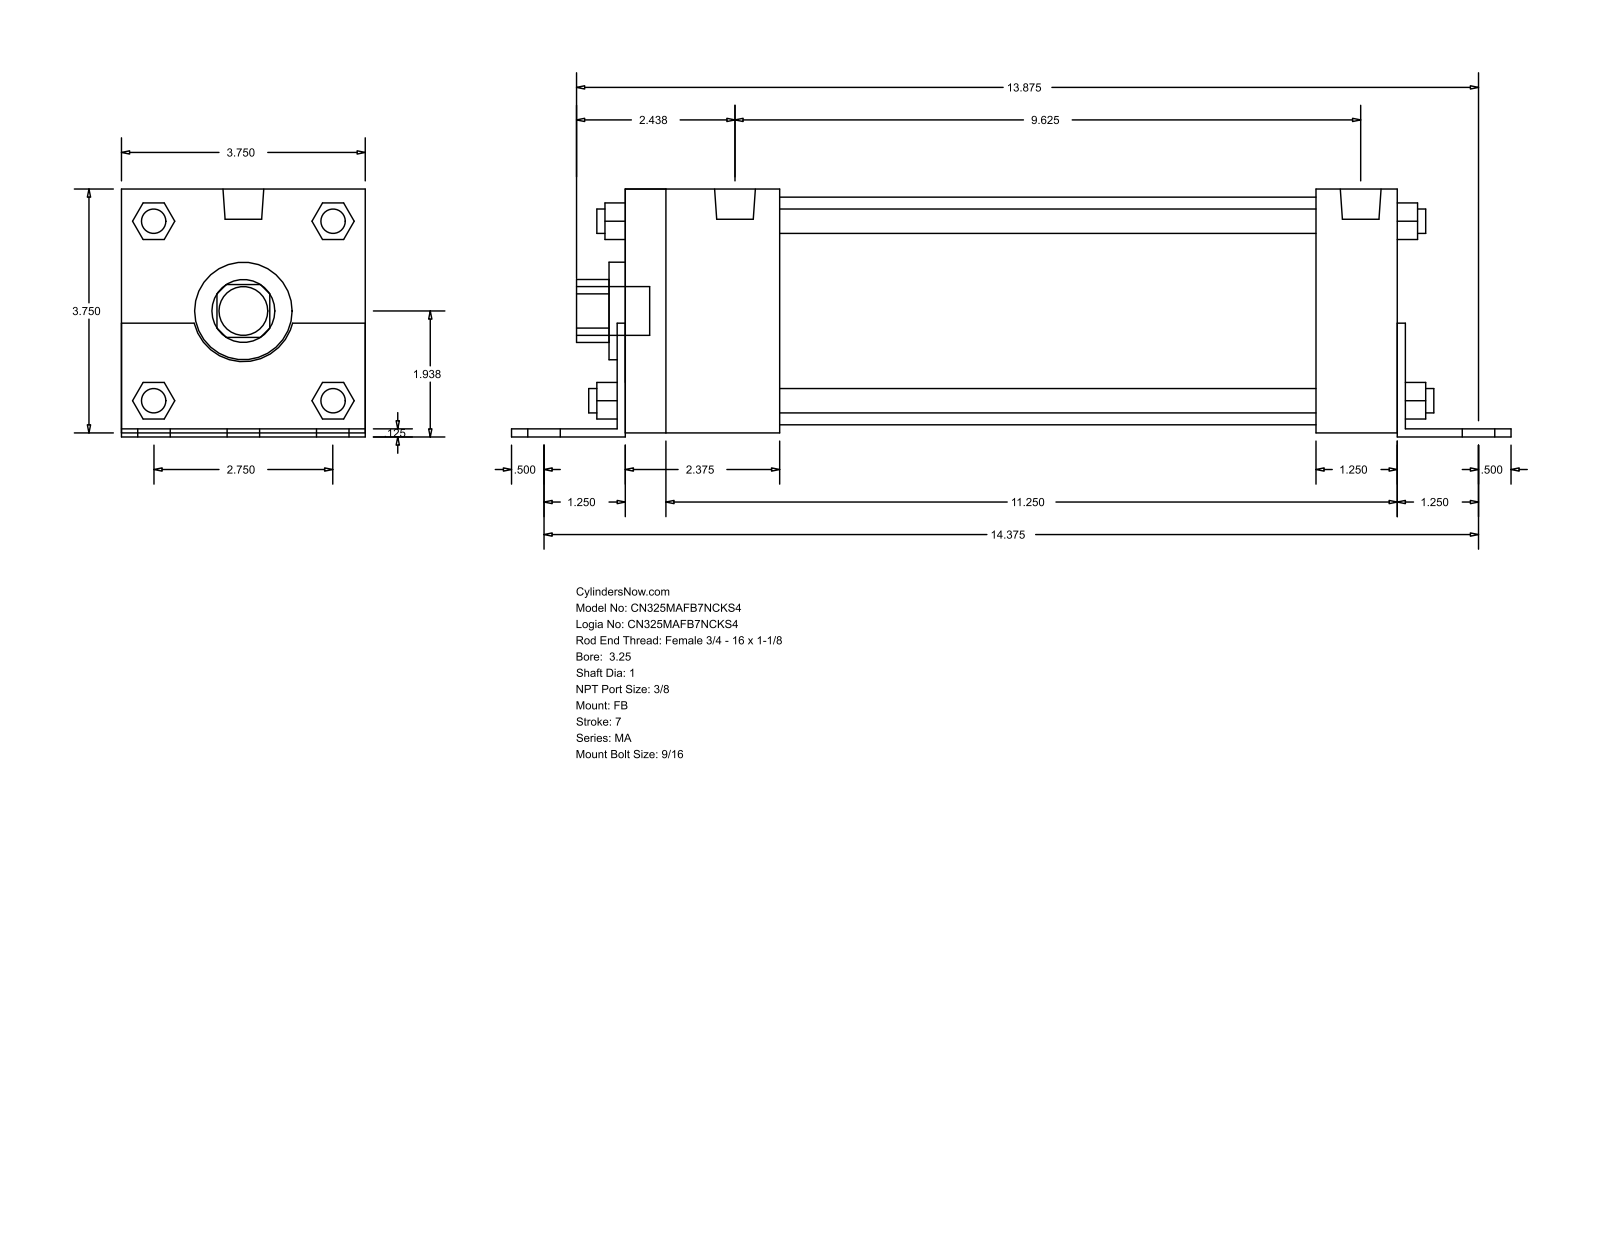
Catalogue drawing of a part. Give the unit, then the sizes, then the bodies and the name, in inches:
Units: inches
Overall size (bounding box): 15.375 × 3.813 × 3.75
Round holes (diameter × count): ⌀1 ×1, ⌀1.5 ×1, ⌀3.5 ×1
Round bosses / shafts (diameter × count): ⌀0.563 ×6, ⌀0.437 ×4, ⌀0.375 ×4, ⌀0.627 ×2, ⌀0.75 ×1
Partial cylindrical surfaces — rounded edges, fillets, slot ends (radius × count): R0.484 ×1, R0.78 ×1
Main face-to-face distances: 3.75, 0.125, 0.063, 3.812, 0.062, 3.687, 12, 11.875, 12.125, 10.75
Bodies: 0 solids, 140 faces (105 planar, 35 cylindrical, 0 other)
Part name (STEP PRODUCT): MA_FB__0325_1
STEP written by: GSSL Pune (CONFIG_CONTROL_DESIGN)
